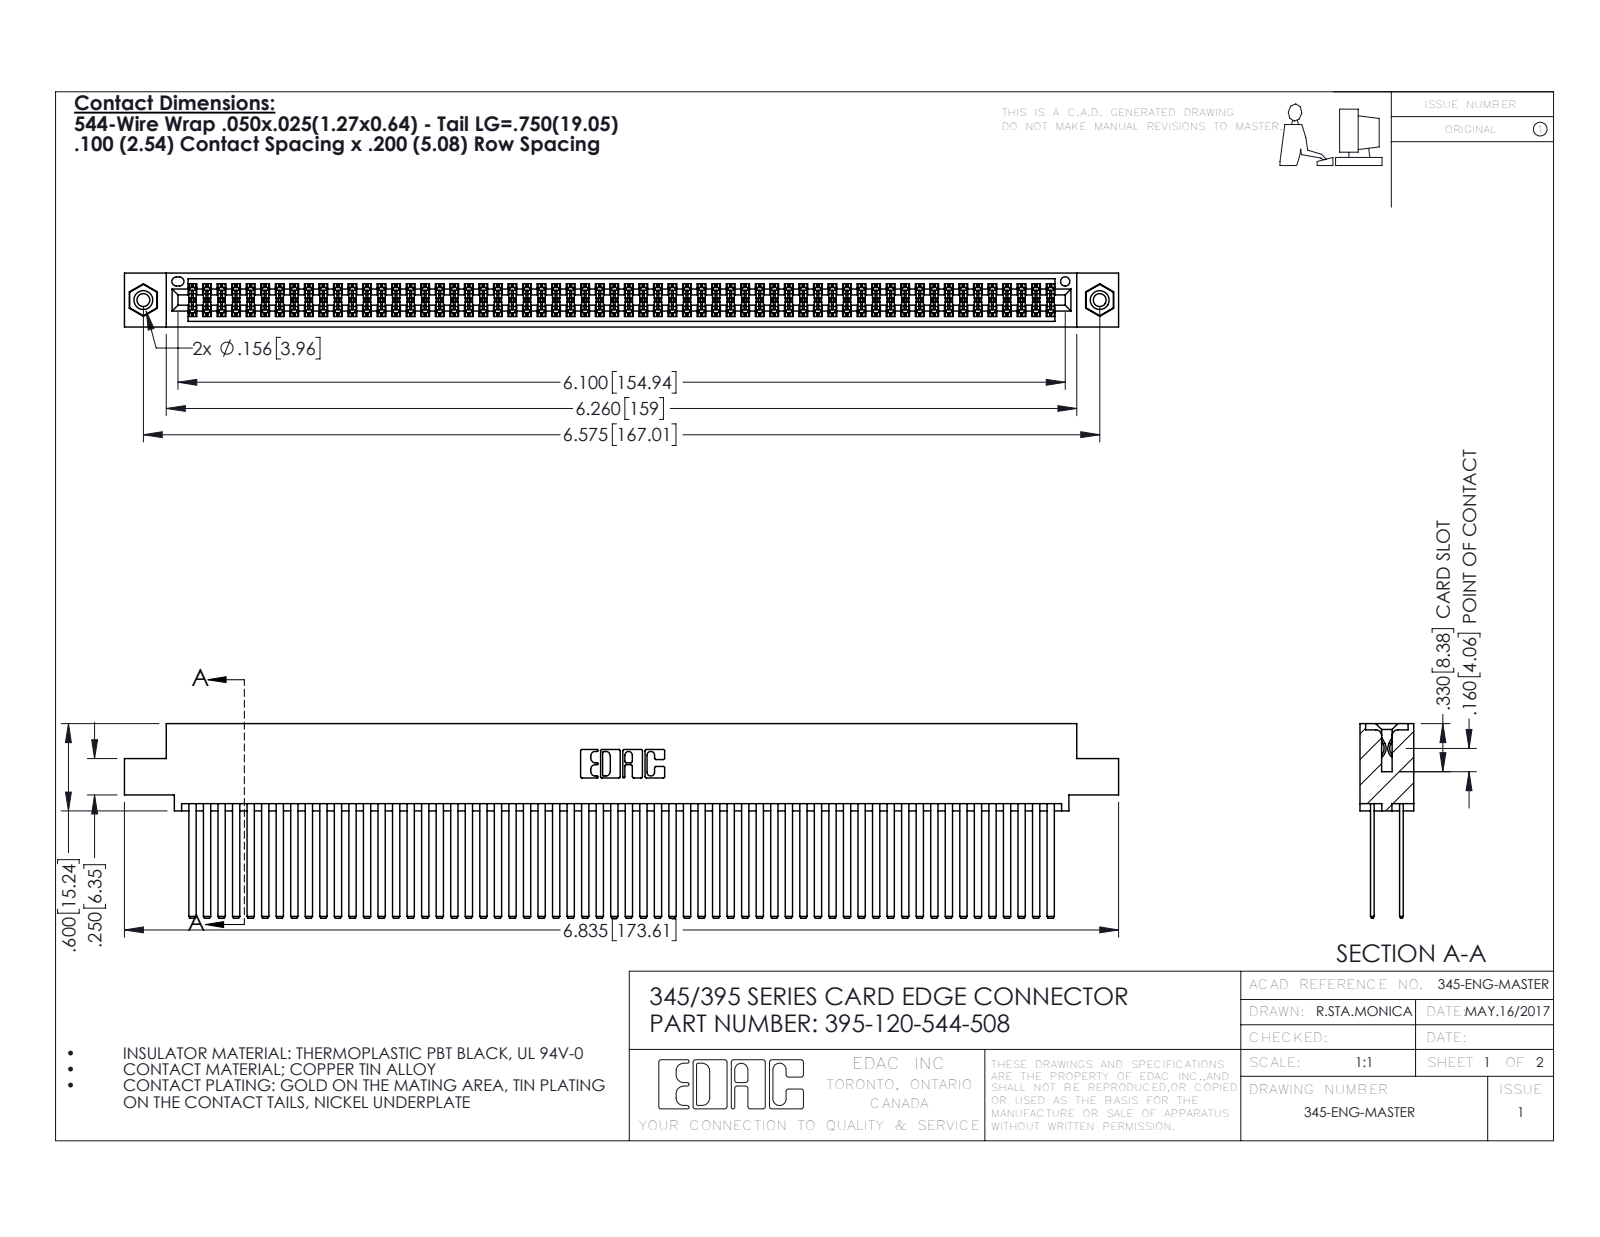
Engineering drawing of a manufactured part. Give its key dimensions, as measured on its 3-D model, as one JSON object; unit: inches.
{"part_name": "345-292-001_345-293-144; 345-250-001_345-250-003-102; 345 Part_0.110 Offset - 0.156 Dia-TI; 395-120-544-508", "step_written_by": "SolidWorks 2016 (CONFIG_CONTROL_DESIGN)", "units": "inches", "bodies": {"solids": 123, "faces": 5470, "planar": 3596, "cylindrical": 1858, "other": 16}, "overall_size": [6.835, 1.337, 0.37], "volume_in3": 1.137, "surface_area_in2": 51.04, "round_holes": [[0.089, 2], [0.125, 2], [0.156, 2], [0.064, 1]], "round_bosses_or_shafts": [[0.155, 2]], "partial_cylinders_radius": [[0.006, 180], [0.01, 22], [0.007, 6], [0.031, 6], [0.026, 3], [0.014, 2], [0.019, 2], [0.022, 2]], "face_to_face_distances": [0.2, 0.025, 0.072, 0.098, 0.272, 0.298, 0.225, 0.175, 0.37, 0.149], "hole_center_spacings": [0.27, 6.339, 6.575]}
